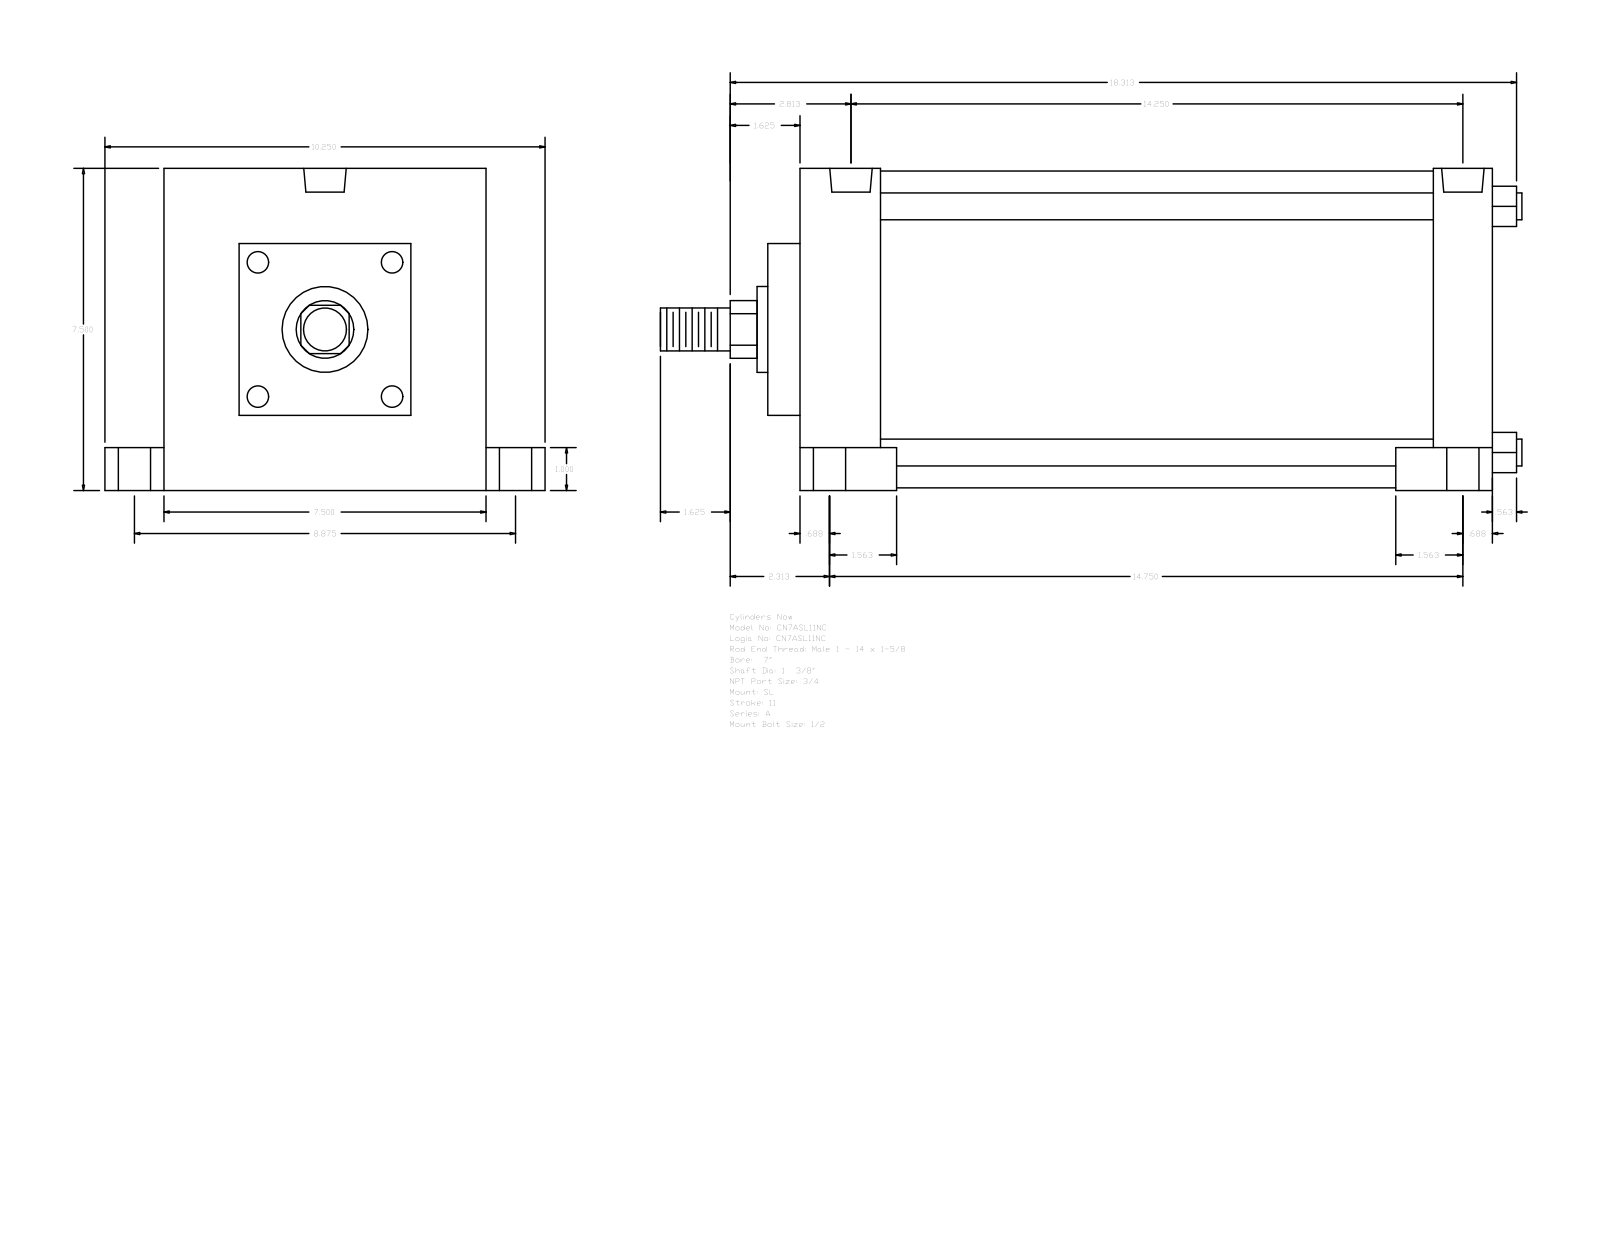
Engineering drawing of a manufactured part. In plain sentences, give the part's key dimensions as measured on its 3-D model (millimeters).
The part is named "A_SL__0700_1.375". Its 3-D file was written by "GSSL Pune (CONFIG_CONTROL_DESIGN)". It is 0 solids with 117 faces: 85 planar, 32 cylindrical and 0 other. Overall it measures 509.59 by 260.35 by 190.5 millimeters. Round holes: 4 of diameter 15.08, 4 of diameter 19.05, 4 of diameter 25.4, 2 of diameter 25.12. Round bosses or shafts: 4 of diameter 15.88, 1 of diameter 187.32, 1 of diameter 50.8, 1 of diameter 34.92, 1 of diameter 25.4. Partial cylindrical surfaces (rounded edges, fillets, slot ends): 1 of radius 17.06. The main face-to-face distances are 190.5, 409.58, 19.04, 428.62, 393.7, 66.67, 47.63, 361.95, 374.66, 327.03. The hole center spacings are 5.56, 112.71, 112.85, 113.42, 114.18, 225.42, 350.83, 356.39.
